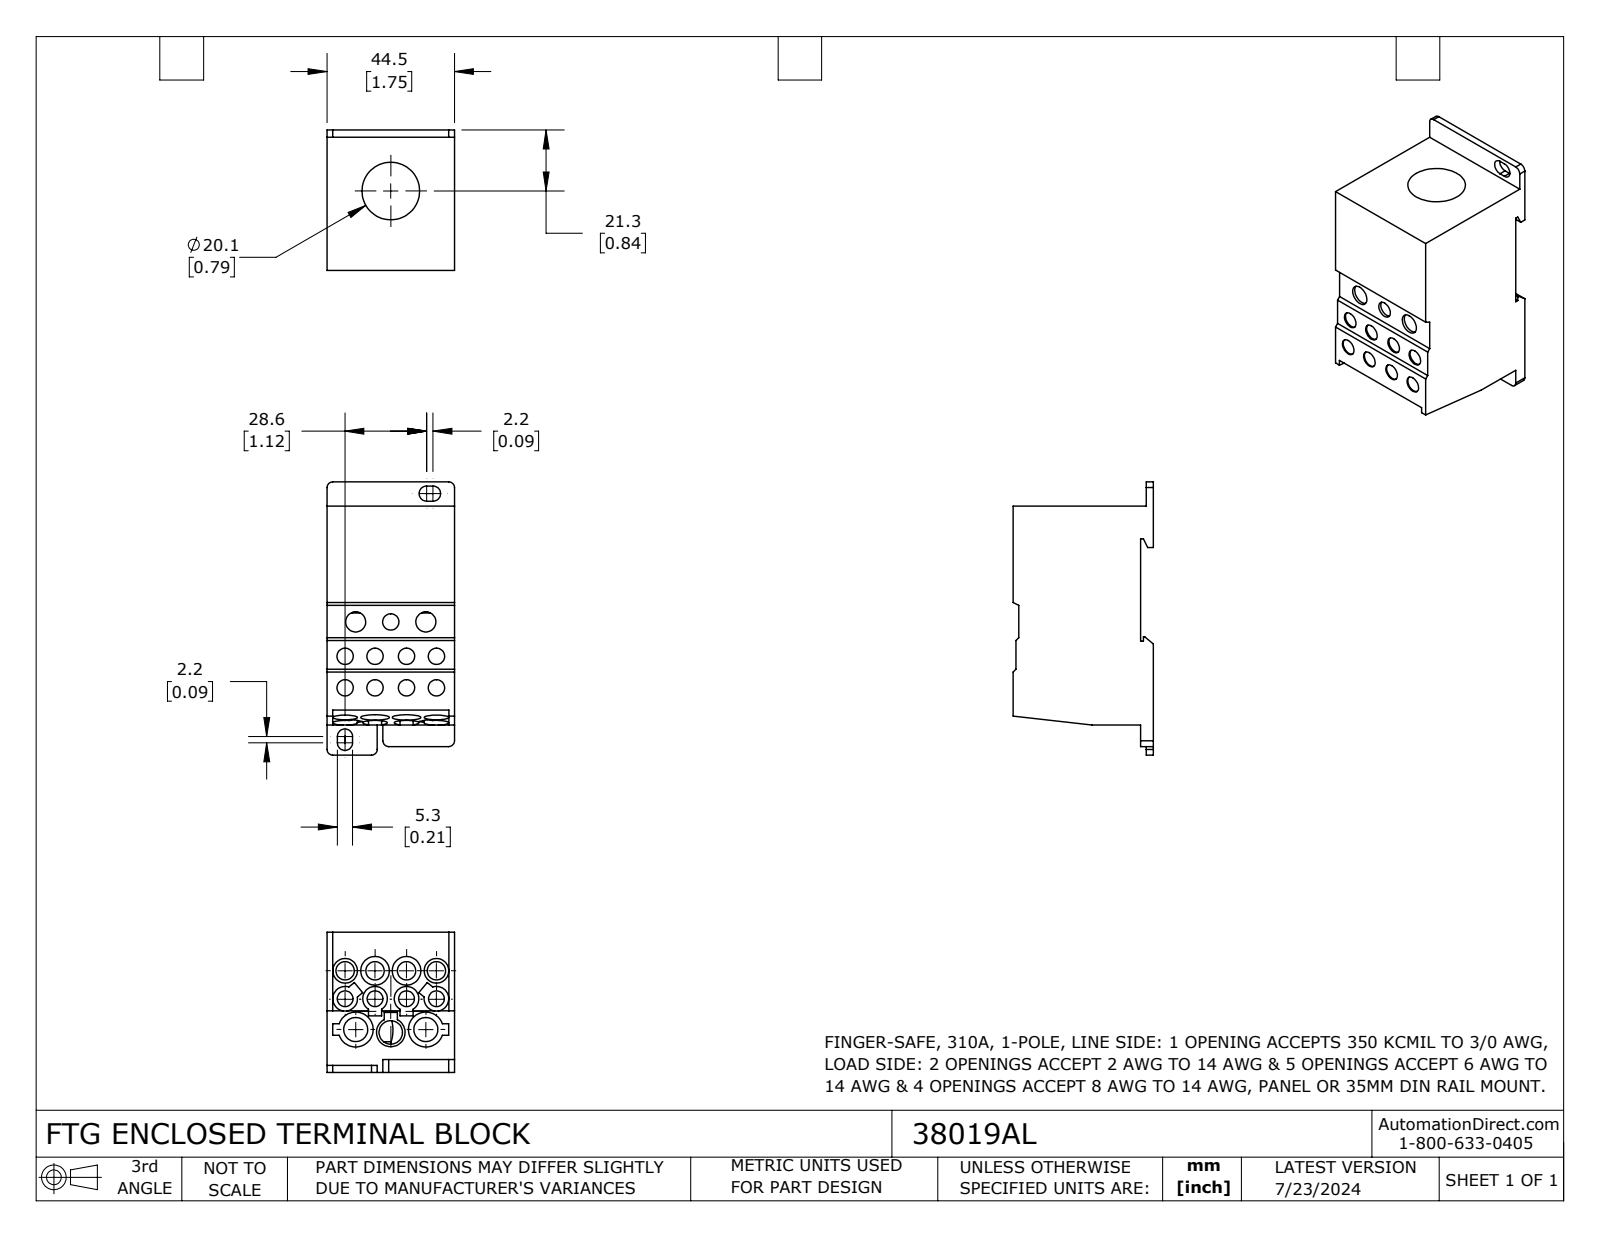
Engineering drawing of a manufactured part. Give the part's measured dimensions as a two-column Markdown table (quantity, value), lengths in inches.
| quantity | value |
| --- | --- |
| part name | 38019AL |
| STEP written by | SolidWorks 2023 (CONFIG_CONTROL_DESIGN) |
| units | inches |
| bodies | 1 solid, 271 faces (127 planar, 97 cylindrical, 47 other) |
| overall size | 3.756 × 1.929 × 1.752 |
| volume | 7.701 in³ |
| surface area | 58.41 in² |
| round holes (diameter × count) | 0.224 × 9, 0.339 × 6, 0.244 × 4, 0.252 × 4, 0.331 × 3, 0.394 × 3, 0.276 × 2, 0.48 × 2, 0.791 × 1 |
| partial cylindrical surfaces (radius × count) | 0.079 × 6, 0.031 × 4, 0.104 × 4, 0.463 × 1, 0.491 × 1 |
| main face-to-face distances | 1.752, 0.079, 1.673, 0.077, 1.675, 1.596, 1.929, 0.177, 1.594, 1.598 |
| hole center spacings | 0.411, 0.844, 0.433, 1.256, 0.931, 0.384, 0.392, 0.563 |
